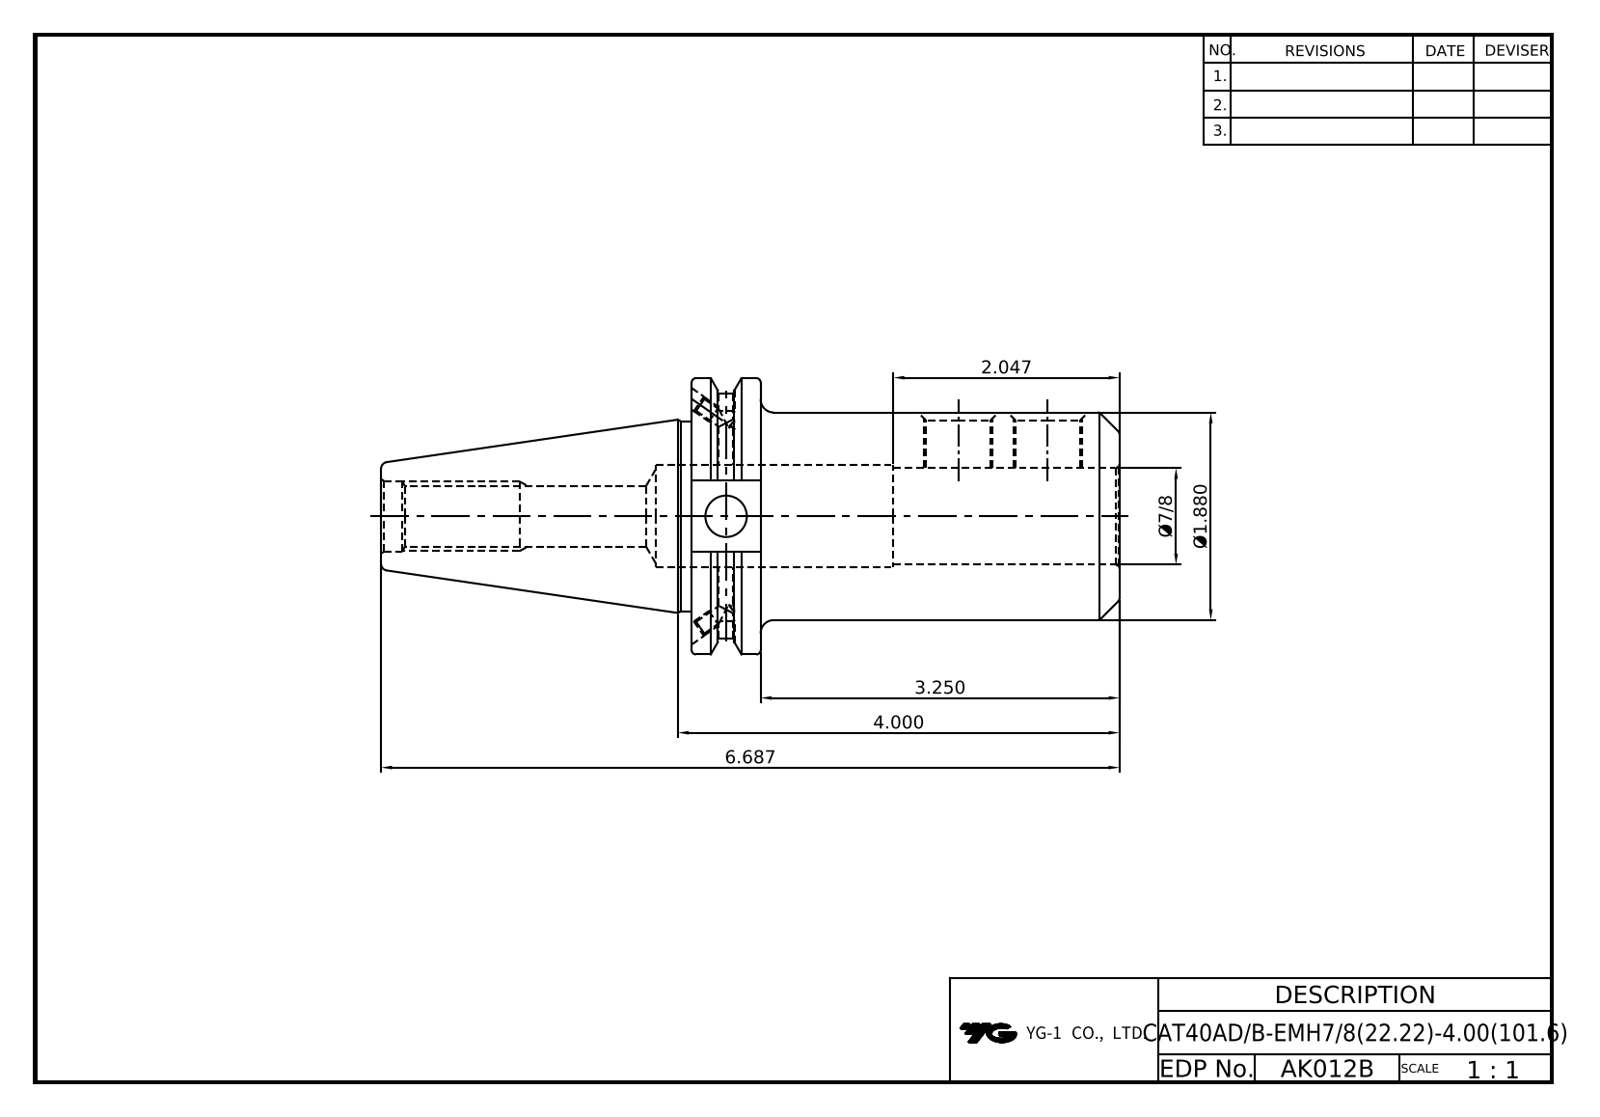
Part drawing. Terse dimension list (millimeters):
name: LO-CAT40ADB-EMH22.225-101.6
written by: Autodesk Inventor 2025 (AUTOMOTIVE_DESIGN)
unit: mm
bodies: 1 solid, 92 faces (37 planar, 32 cylindrical, 23 other)
size: 169.85 × 63.5 × 61.09
volume: 201 744 mm³; area: 39 765 mm²
holes: 4× ⌀3.24, 2× ⌀4, 2× ⌀4.2, 2× ⌀14.35, 1× ⌀9.53, 1× ⌀13.39, 1× ⌀16.3, 1× ⌀22.23, 1× ⌀23.43
bosses: 1× ⌀63.5, 1× ⌀47.75, 1× ⌀43.6
rounds: 1× R8.19, 1× R28.15
face distances: 98.43, 15.88, 82.55, 8.25, 24.13, 106.68, 47.6, 16.38, 63.17, 71.42
hole spacings: 20.6
